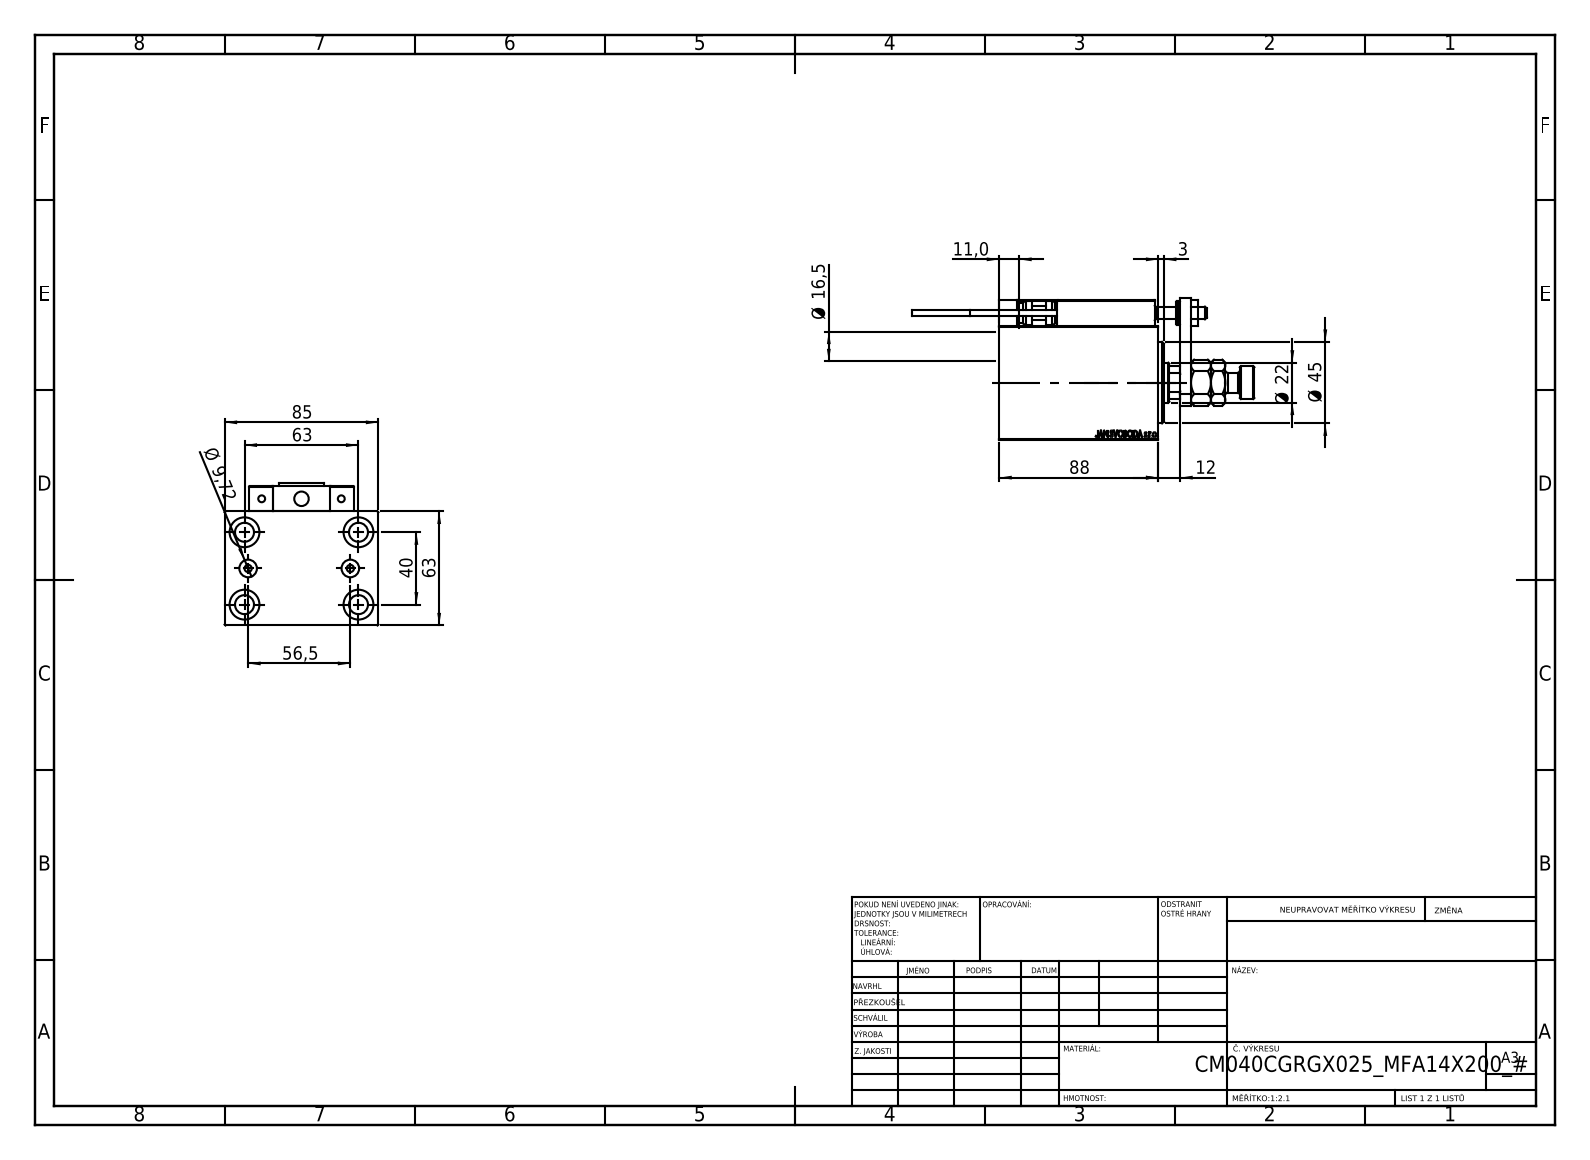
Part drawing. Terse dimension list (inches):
name: SWITCH_X_FRONT_BACK; MAGNET; X_Y_MFA; SWITCH X (+7 more)
written by: SolidWorks 2019 (CONFIG_CONTROL_DESIGN)
unit: in
bodies: 24 solids, 1330 faces (576 planar, 188 cylindrical, 566 other)
size: 7.441 × 3.346 × 3.091
volume: 28.59 in³; area: 164.7 in²
holes: 6× ⌀0.157, 5× ⌀0.315, 5× ⌀0.65, 4× ⌀0.126, 4× ⌀0.413, 2× ⌀0.197, 2× ⌀0.383, 1× ⌀0.276, 1× ⌀0.492, 1× ⌀0.866, 1× ⌀1.004, 1× ⌀1.575
bosses: 2× ⌀0.433, 2× ⌀0.197, 2× ⌀0.15, 1× ⌀0.709, 1× ⌀0.512
rounds: 30× R0.012, 2× R0.118, 1× R0.413
face distances: 2.48, 0.472, 3.346, 2.992, 3.465, 0.551, 3.031, 0.709, 0.984, 1.181
hole spacings: 1.469, 0.448, 0.787, 0.791, 0.807, 1.165, 1.169, 1.42
